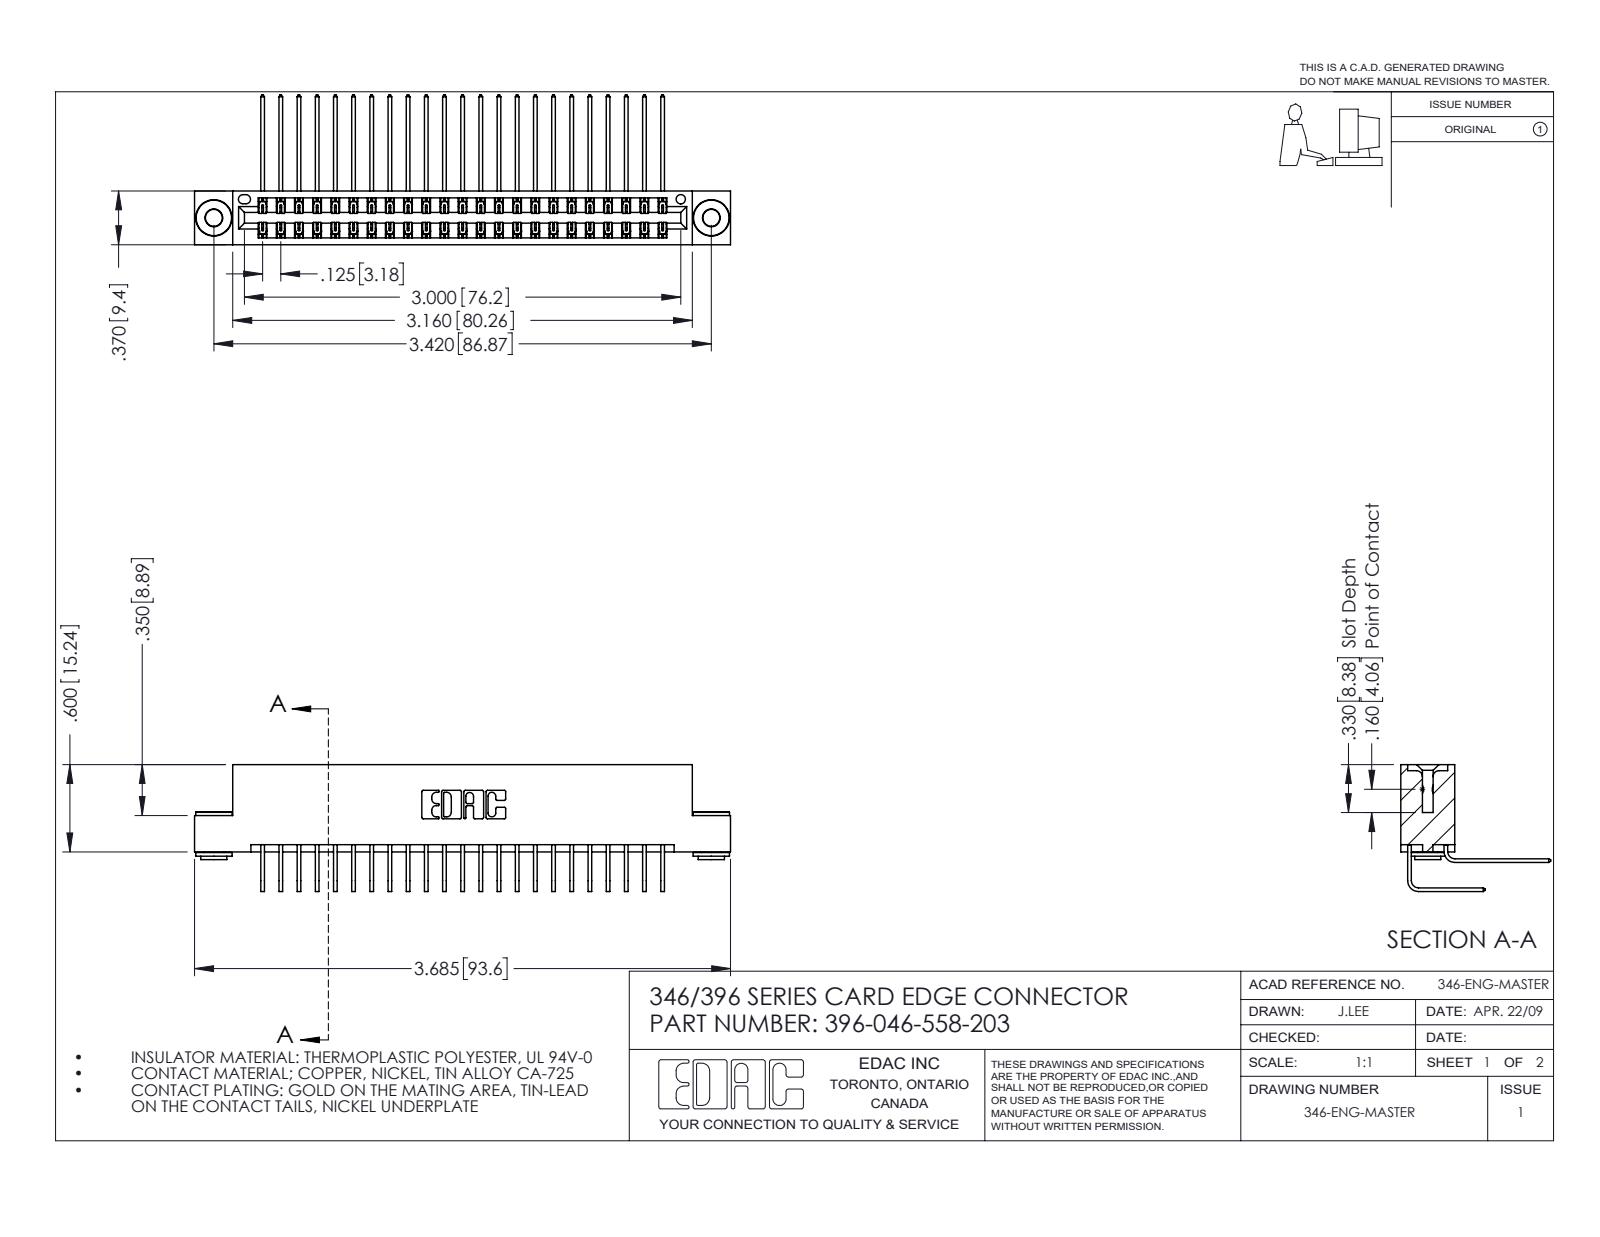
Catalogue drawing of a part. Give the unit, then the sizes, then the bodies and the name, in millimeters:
Units: millimetres
Overall size (bounding box): 93.6 × 26.2 × 22.2
Round holes (diameter × count): ⌀2.9 ×2, ⌀4 ×2, ⌀1.6 ×1
Round bosses / shafts (diameter × count): ⌀6.4 ×2, ⌀4.6 ×2, ⌀3.5 ×2
Partial cylindrical surfaces — rounded edges, fillets, slot ends (radius × count): R0.2 ×69, R0.3 ×22, R0.2 ×6, R0.8 ×6, R0.7 ×3, R0.4 ×2, R0.6 ×2, R0.6 ×2
Main face-to-face distances: 8.2, 1.2, 6.4, 0.6, 9.4, 7.6, 1.8, 7, 3.8, 5.6
Hole centre spacings: 6.2, 81.6, 86.9
Volume: 9 260 mm³ · Surface area: 13 920 mm²
Bodies: 49 solids, 2644 faces (1788 planar, 848 cylindrical, 8 other)
Part name (STEP PRODUCT): 345-292-001_558 559 Tail - 1; 396-046-558-203; 345-292-001_558 Tail - 2; 345-250-002_345-250-002-102 (+1 more)
STEP written by: SolidWorks 2016 (CONFIG_CONTROL_DESIGN)
